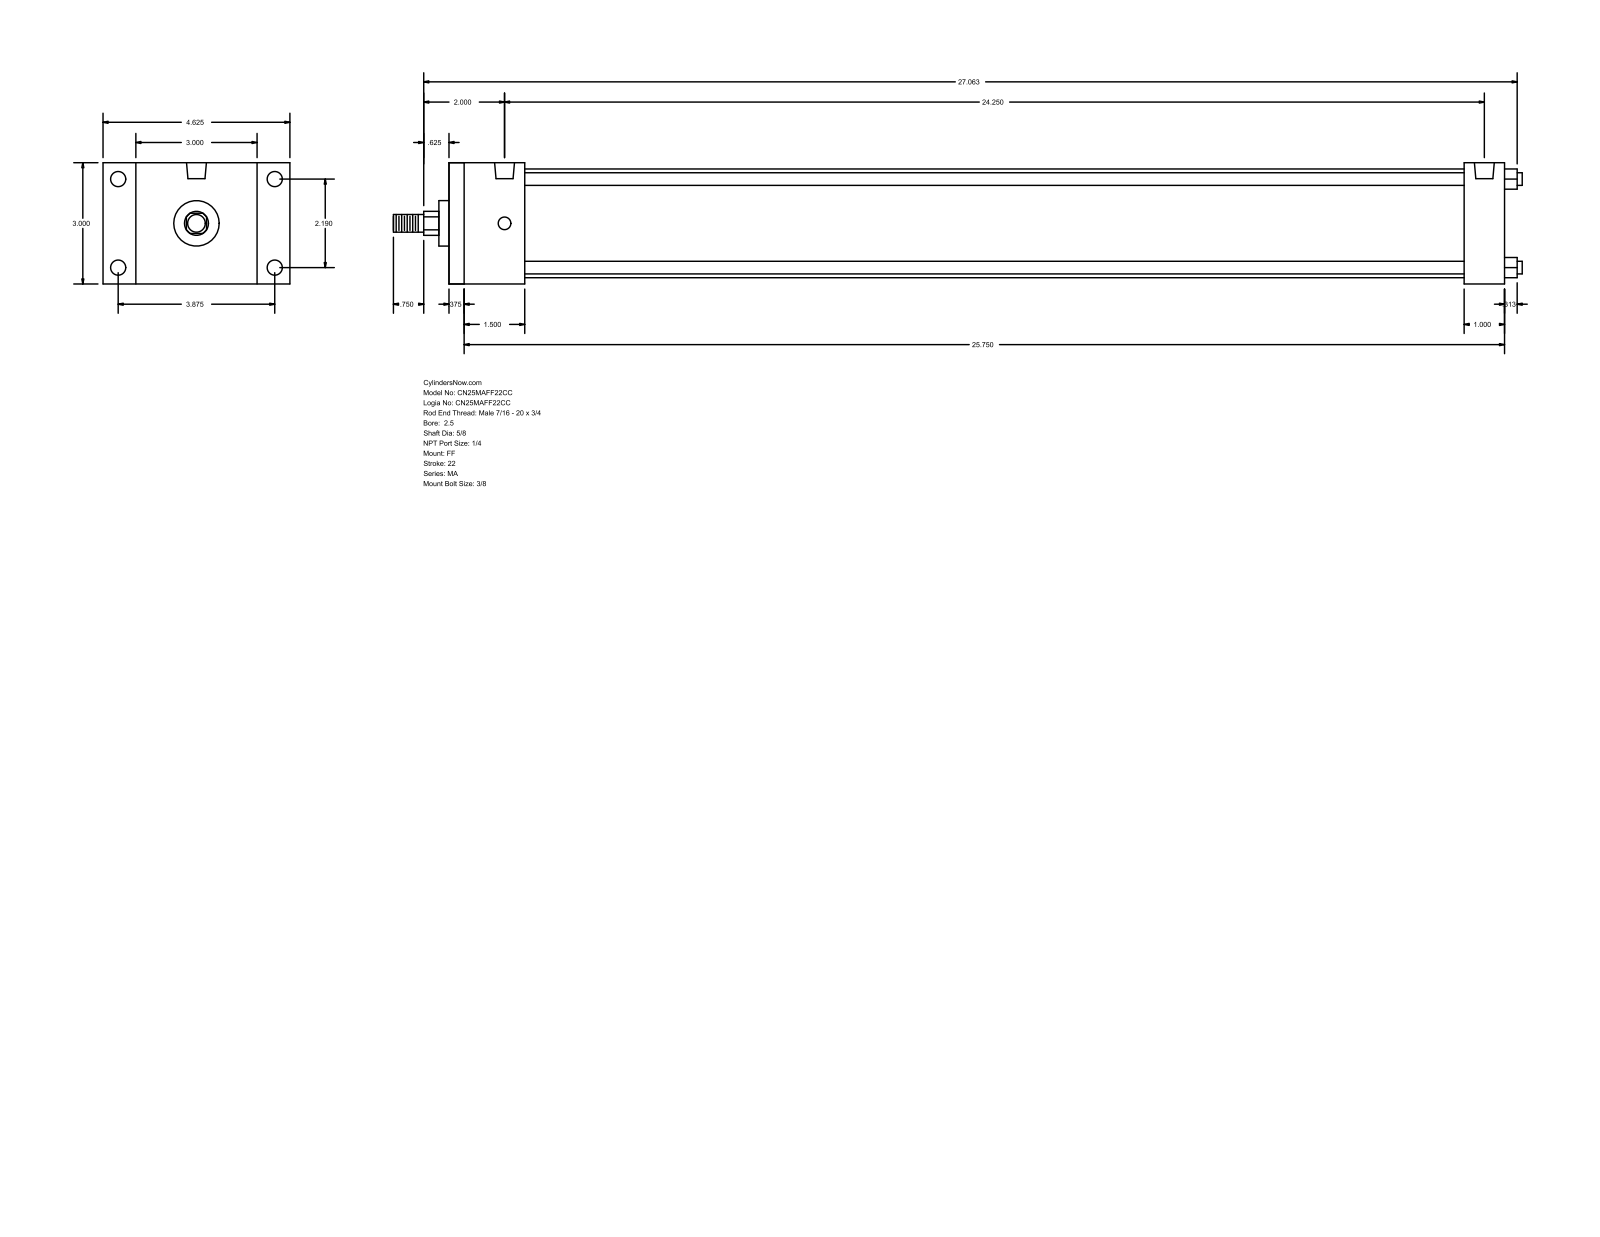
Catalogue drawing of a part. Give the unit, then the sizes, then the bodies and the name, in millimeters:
Units: millimetres
Overall size (bounding box): 709.61 × 117.47 × 76.2
Round holes (diameter × count): ⌀7.94 ×4, ⌀9.53 ×4, ⌀12.49 ×2
Round bosses / shafts (diameter × count): ⌀7.94 ×4, ⌀68.33 ×1, ⌀28.57 ×1, ⌀15.88 ×1, ⌀11.11 ×1
Partial cylindrical surfaces — rounded edges, fillets, slot ends (radius × count): R7.54 ×1
Main face-to-face distances: 76.2, 663.57, 654.05, 9.52, 25.4, 47.62, 638.17, 38.1, 628.65, 590.55
Hole centre spacings: 55.62, 98.42, 113.05, 615.95
Bodies: 0 solids, 92 faces (64 planar, 28 cylindrical, 0 other)
Part name (STEP PRODUCT): MA_FF__0250_0.625
STEP written by: GSSL Pune (CONFIG_CONTROL_DESIGN)
